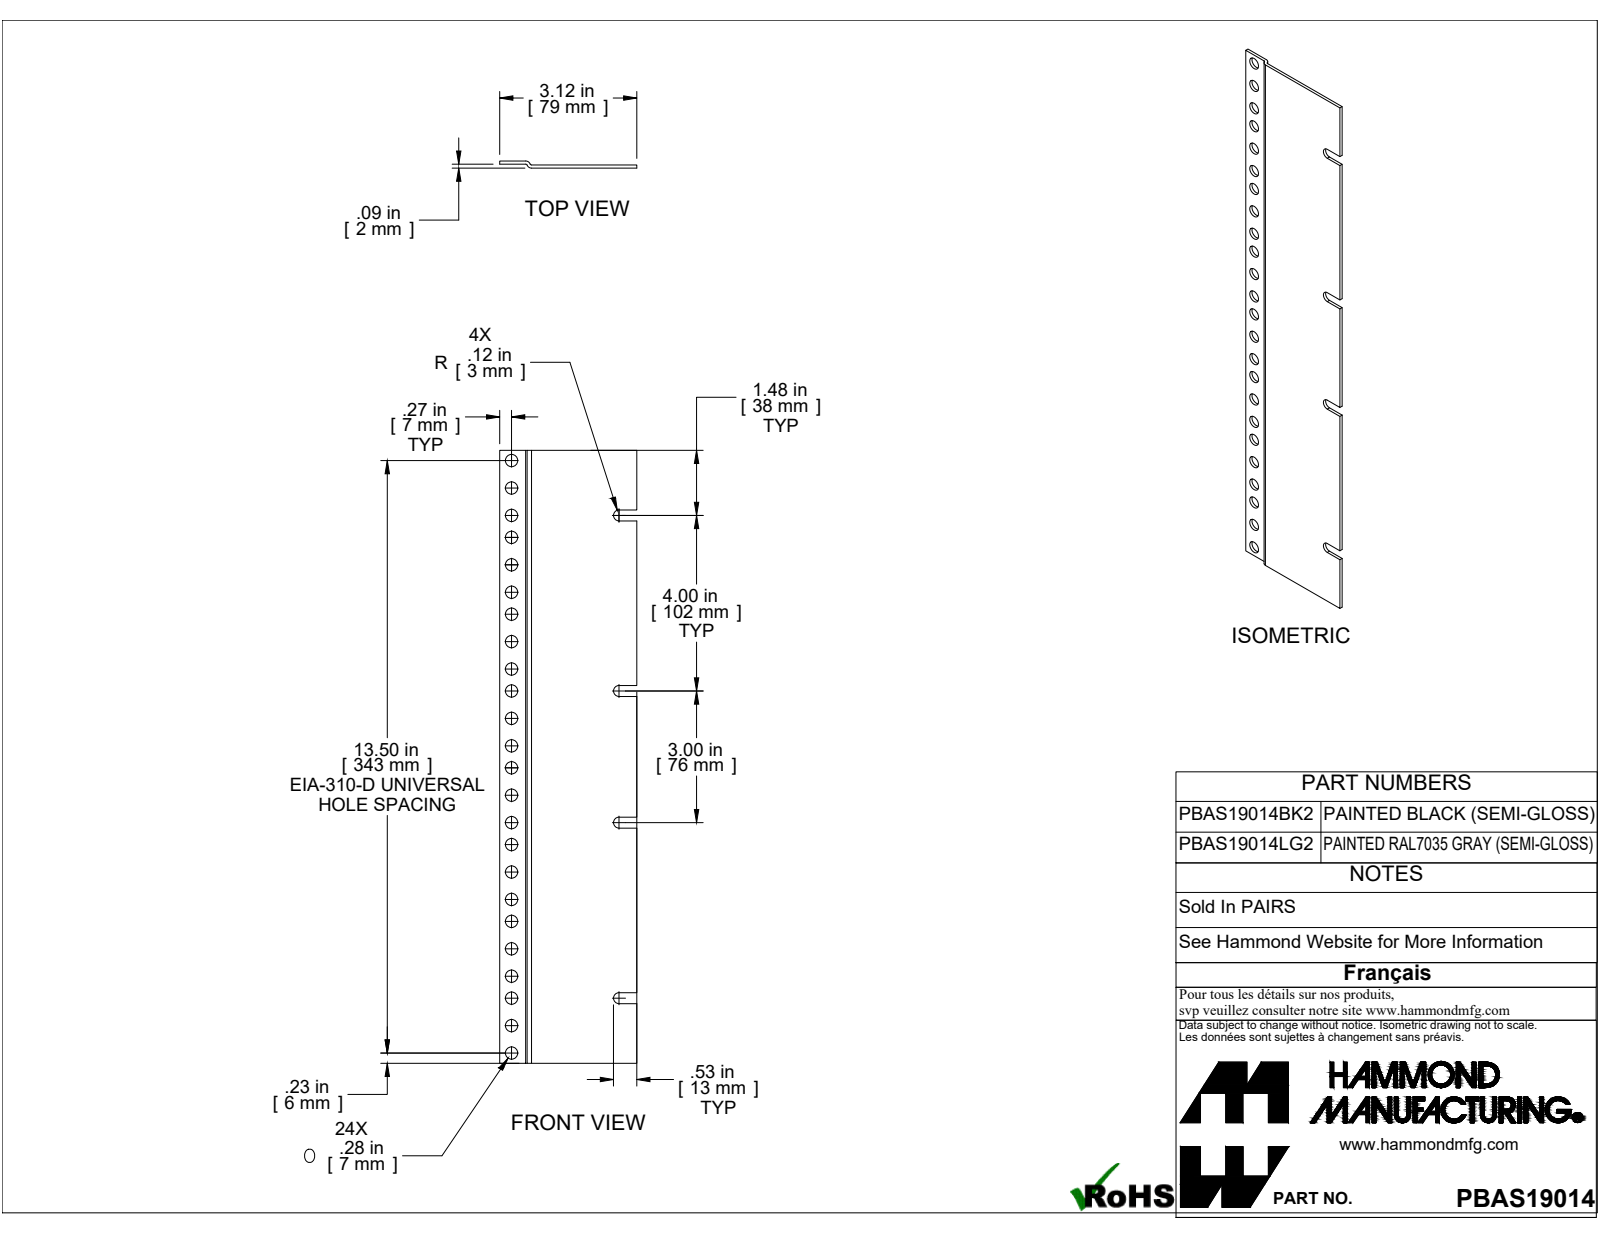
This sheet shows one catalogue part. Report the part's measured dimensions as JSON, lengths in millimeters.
{"part_name": "PBAS19014LG2", "step_written_by": "SolidWorks 2019 (CONFIG_CONTROL_DESIGN)", "units": "millimeters", "bodies": {"solids": 1, "faces": 52, "planar": 20, "cylindrical": 32, "other": 0}, "overall_size": [354.8, 79.4, 4.1], "volume_mm3": 49770, "surface_area_mm2": 57180, "round_holes": [[7.1, 24]], "partial_cylinders_radius": [[3.2, 4], [0.9, 2], [2.7, 2]], "face_to_face_distances": [1.8, 2.3, 4.1, 0.5, 2.3, 1.8, 79.4, 354.8, 101.6, 6.4], "hole_center_spacings": [44.5, 88.9, 133.4, 15.9, 15.9, 28.6, 31.8, 60.3]}
